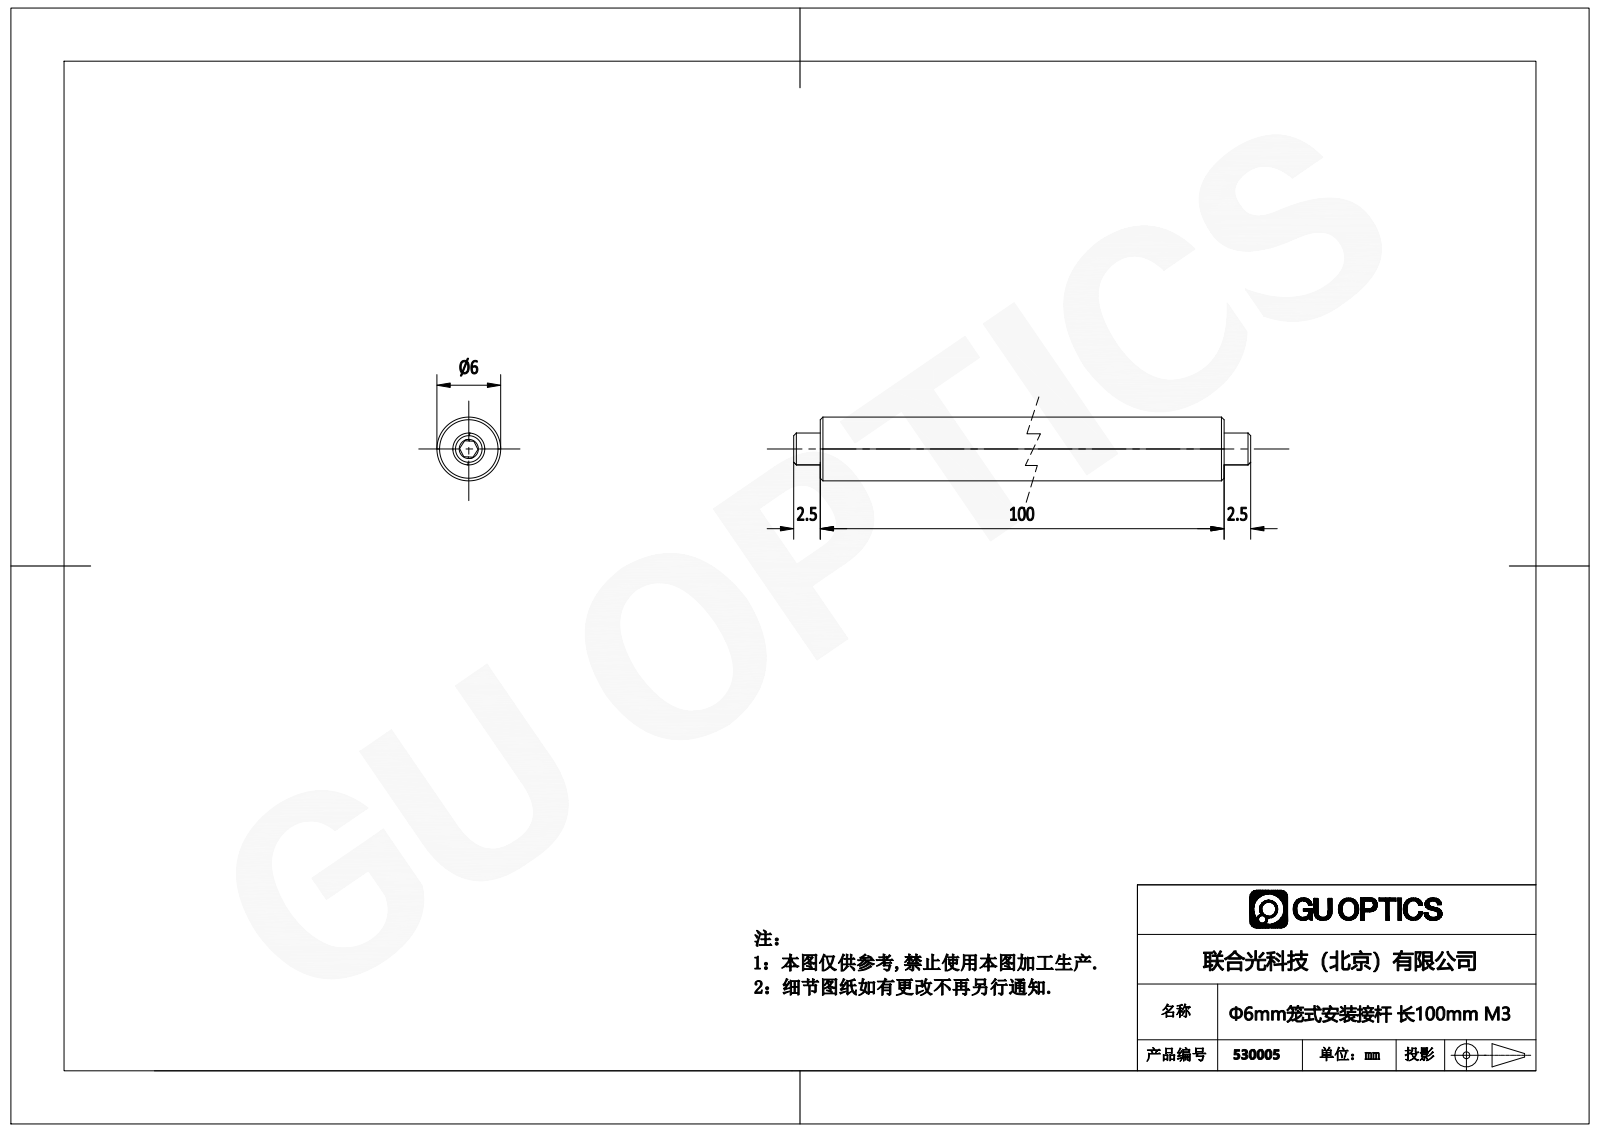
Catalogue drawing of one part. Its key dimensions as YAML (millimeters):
step_written_by: "SolidWorks 2018 (AUTOMOTIVE_DESIGN)"
units: millimeters
bodies: {solids: 0, faces: 36, planar: 18, cylindrical: 6, other: 12}
overall_size: [105, 6, 6]
round_bosses_or_shafts:
  - {diameter: 6, count: 1}
  - {diameter: 3, count: 1}
face_to_face_distances: [100, 1.5, 2.5, 102.5, 1, 104, 101.5, 105, 103]
